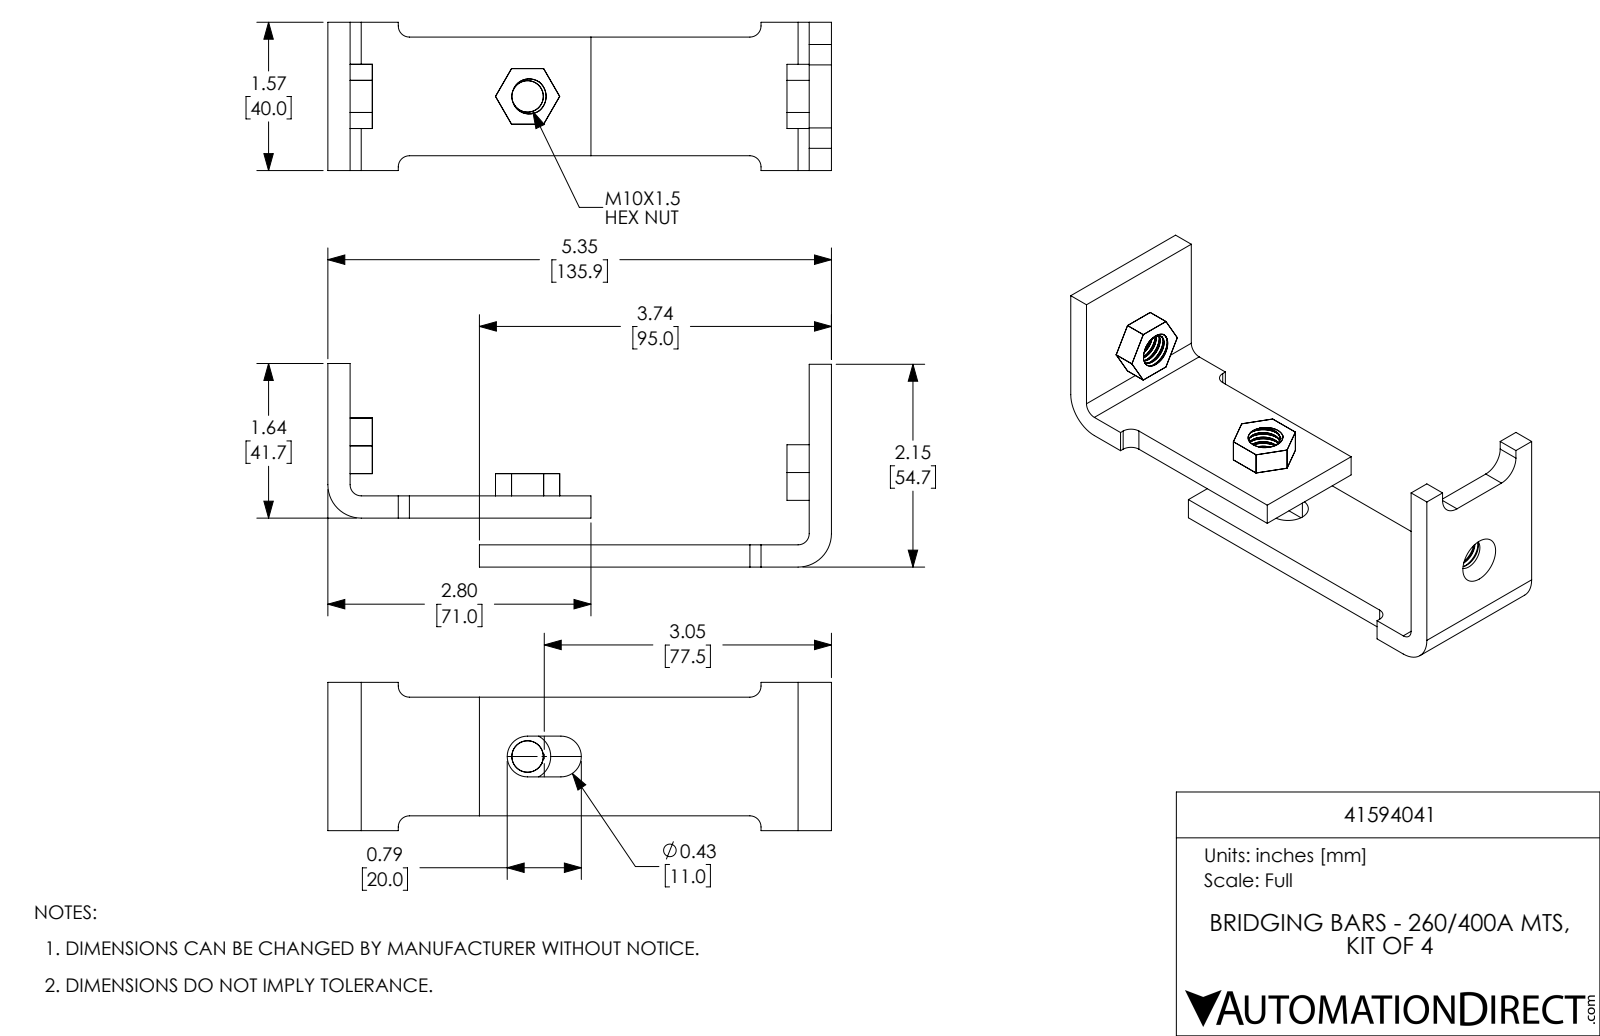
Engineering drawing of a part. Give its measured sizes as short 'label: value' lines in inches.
name: 41594041
written by: SolidWorks 2017 (AUTOMOTIVE_DESIGN)
unit: in
bodies: 7 solids, 233 faces (80 planar, 143 cylindrical, 10 other)
size: 5.35 × 2.162 × 1.575
volume: 3.208 in³; area: 40.43 in²
holes: 3× ⌀0.335, 3× ⌀0.394, 3× ⌀0.492
bosses: 3× ⌀0.512
rounds: 6× R0.118, 4× R0.217, 2× R0.354
face distances: 0.236, 0.52, 5.114, 0.756, 0.284, 0.157, 4.878, 1.417, 5.35, 0.591
hole spacings: 0.284
